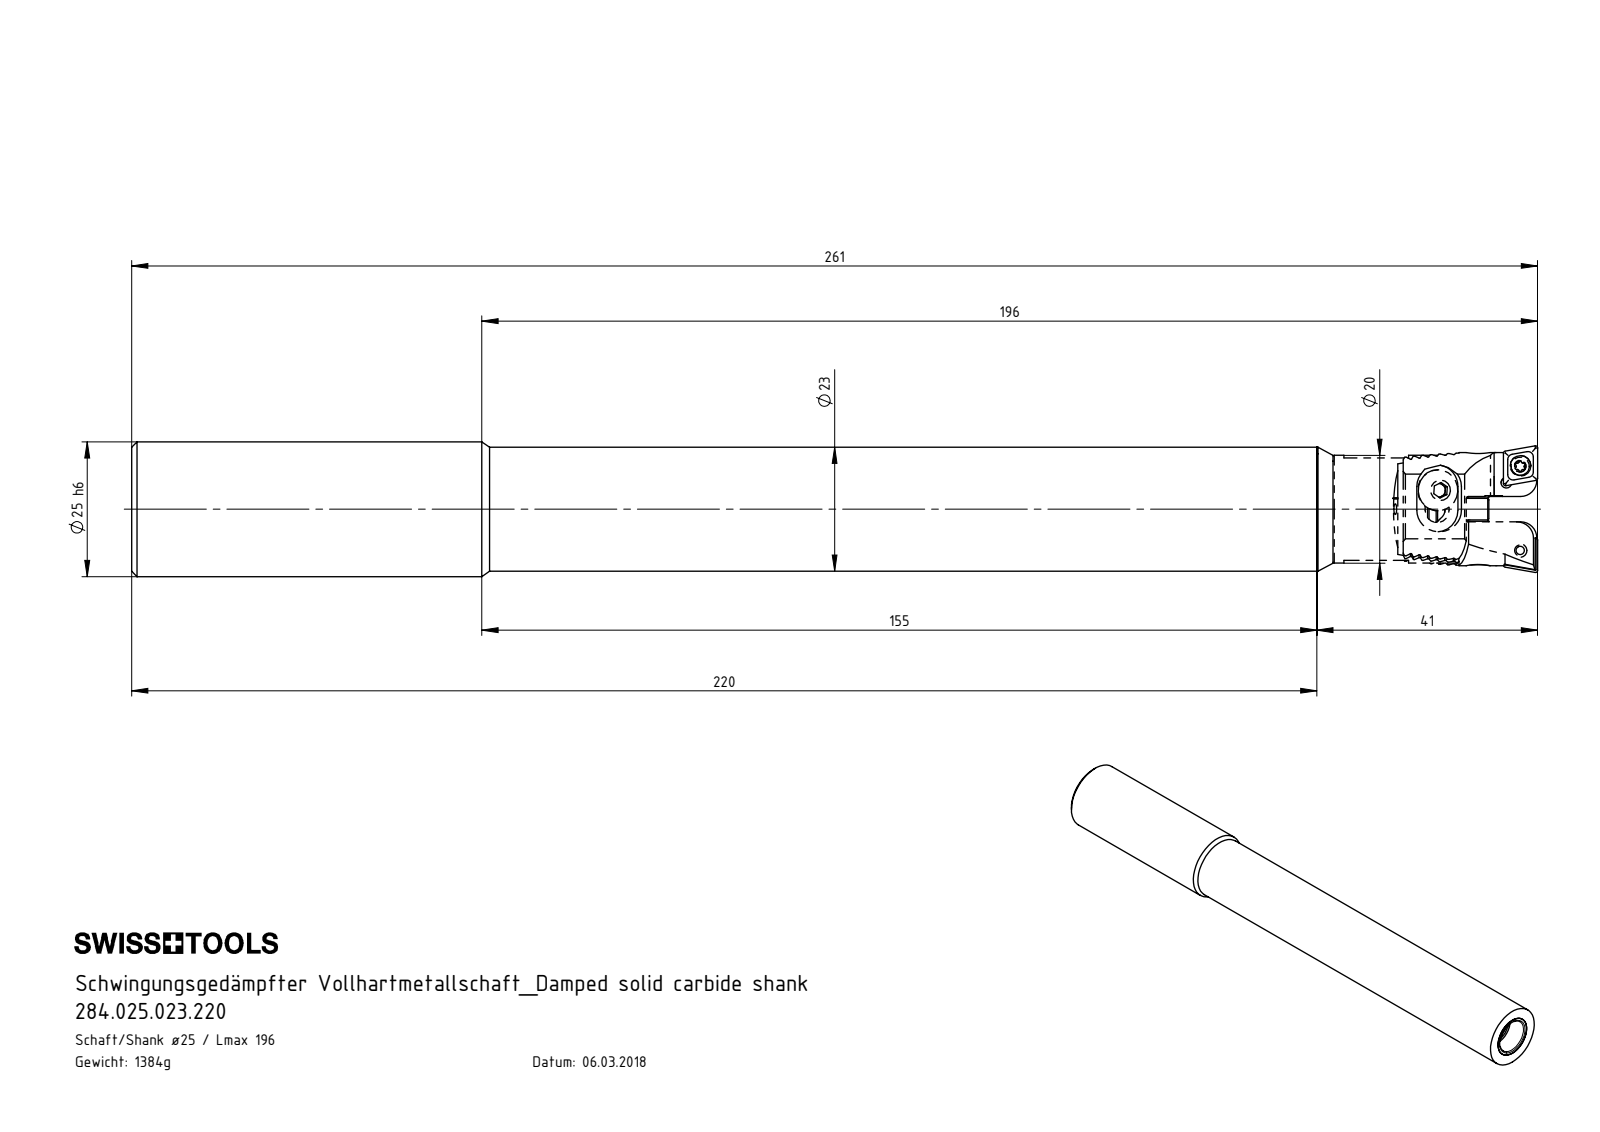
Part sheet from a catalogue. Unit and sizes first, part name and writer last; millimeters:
Units: millimetres
Overall size (bounding box): 260.96 × 25 × 25
Round holes (diameter × count): ⌀2 ×6, ⌀3.3 ×3, ⌀1 ×2, ⌀2.05 ×2, ⌀2.8 ×2, ⌀3.85 ×2, ⌀5 ×2, ⌀2.5 ×1, ⌀3.5 ×1, ⌀4.2 ×1, ⌀6.8 ×1, ⌀8.5 ×1
Round bosses / shafts (diameter × count): ⌀4 ×4, ⌀7.6 ×2, ⌀3.4 ×2, ⌀2.5 ×2, ⌀25 ×1, ⌀23 ×1, ⌀20 ×1, ⌀12 ×1
Partial cylindrical surfaces — rounded edges, fillets, slot ends (radius × count): R0.12 ×26, R0.21 ×12, R0.36 ×10, R1 ×8, R0.5 ×4, R2.3 ×4, R4 ×4, R0.36 ×2
Main face-to-face distances: 1.43, 2.86, 220, 4.29, 3, 223, 5.72, 7.15, 185, 35
Hole centre spacings: 3.99, 4.09, 6, 13.08, 13.17, 15.96, 9.77, 11.6
Volume: 102 230 mm³ · Surface area: 33 704 mm²
Bodies: 16 solids, 808 faces (346 planar, 245 cylindrical, 217 other)
Part name (STEP PRODUCT): Z20-ER3.001.007_A; CCMT060204; WCA-ER2.001.006_B; Z20-WCA.001.015_A (+8 more)
STEP written by: SolidWorks 2017 (CONFIG_CONTROL_DESIGN)
